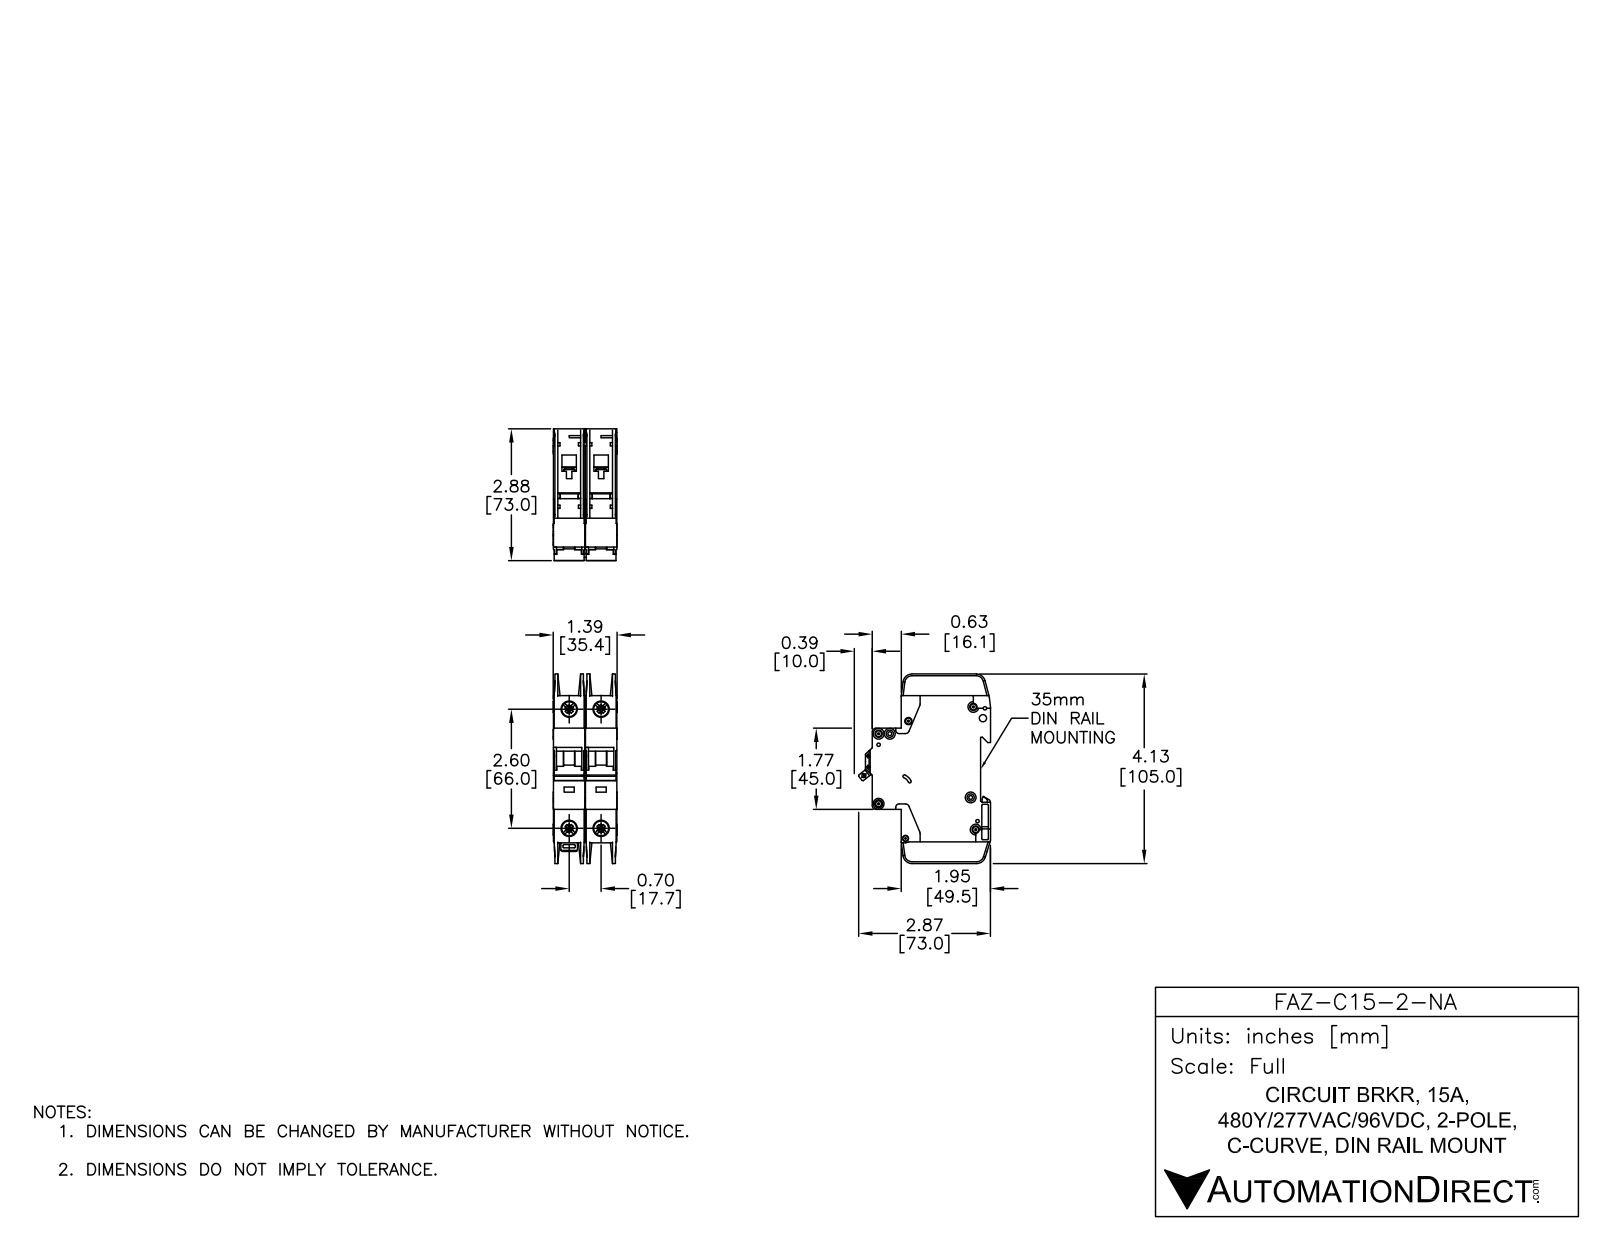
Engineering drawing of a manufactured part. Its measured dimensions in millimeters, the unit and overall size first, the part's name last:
Units: millimetres
Overall size (bounding box): 105 × 73.04 × 35.4
Round holes (diameter × count): ⌀3.6 ×7, ⌀7.15 ×4, ⌀8.2 ×4, ⌀1.09 ×2, ⌀1.5 ×2, ⌀4 ×2, ⌀1.9 ×1, ⌀2.15 ×1, ⌀2.2 ×1, ⌀2.55 ×1, ⌀3.3 ×1, ⌀3.4 ×1
Round bosses / shafts (diameter × count): ⌀6 ×7, ⌀2.5 ×2
Partial cylindrical surfaces — rounded edges, fillets, slot ends (radius × count): R0.25 ×47, R0.5 ×24, R1 ×18, R2 ×12, R5 ×5, R1.8 ×4, R4 ×4, R0.2 ×2
Main face-to-face distances: 17.7, 17.5, 0.7, 15.05, 2.45, 1.75, 15.75, 13.3, 35.2, 17
Hole centre spacings: 6.2, 17.7, 66, 68.33, 5.19, 6.1, 8.19, 8.56
Volume: 155 390 mm³ · Surface area: 49 479 mm²
Bodies: 6 solids, 1568 faces (818 planar, 526 cylindrical, 224 other)
Part name (STEP PRODUCT): FAZ-C15-2-NA
STEP written by: SolidWorks 2014 (AUTOMOTIVE_DESIGN)
